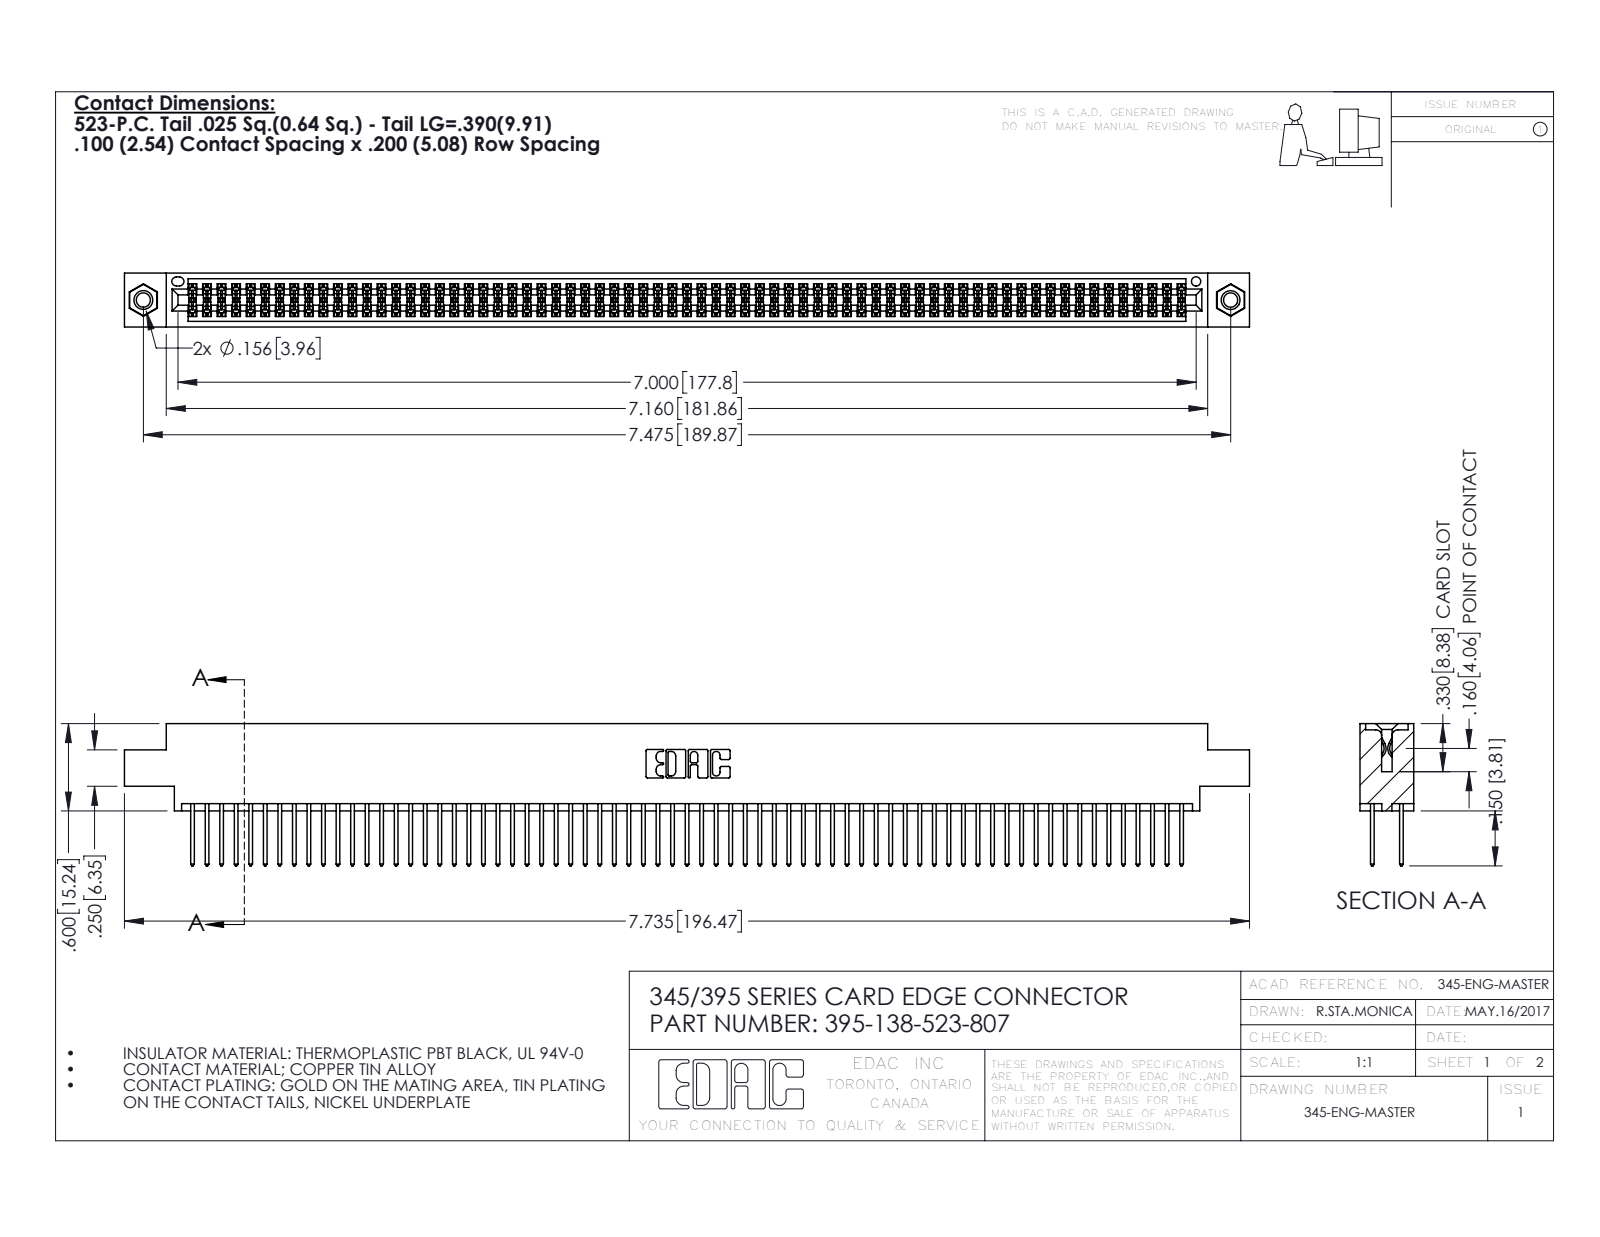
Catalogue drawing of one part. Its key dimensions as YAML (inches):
part_name: "345-250-001_345-250-005-103; 345 Part_0.170 Offset - 0.156 Dia-TI; 395-138-523-807; 345-292-001_345-293-123"
step_written_by: "SolidWorks 2016 (CONFIG_CONTROL_DESIGN)"
units: inches
bodies: {solids: 141, faces: 7090, planar: 4670, cylindrical: 2404, other: 16}
overall_size: [7.735, 0.977, 0.37]
volume: 1.189
surface_area: 47.7
round_holes:
  - {diameter: 0.098, count: 2}
  - {diameter: 0.125, count: 2}
  - {diameter: 0.156, count: 2}
  - {diameter: 0.064, count: 1}
round_bosses_or_shafts:
  - {diameter: 0.155, count: 2}
partial_cylinders:
  - {radius: 0.006, count: 207}
  - {radius: 0.01, count: 138}
  - {radius: 0.01, count: 22}
  - {radius: 0.007, count: 6}
  - {radius: 0.031, count: 6}
  - {radius: 0.026, count: 3}
  - {radius: 0.014, count: 2}
  - {radius: 0.019, count: 2}
face_to_face_distances: [0.072, 0.298, 0.2, 0.098, 0.272, 0.025, 0.37, 0.225, 0.175, 0.149]
hole_center_spacings: [0.27, 7.239, 7.475]
